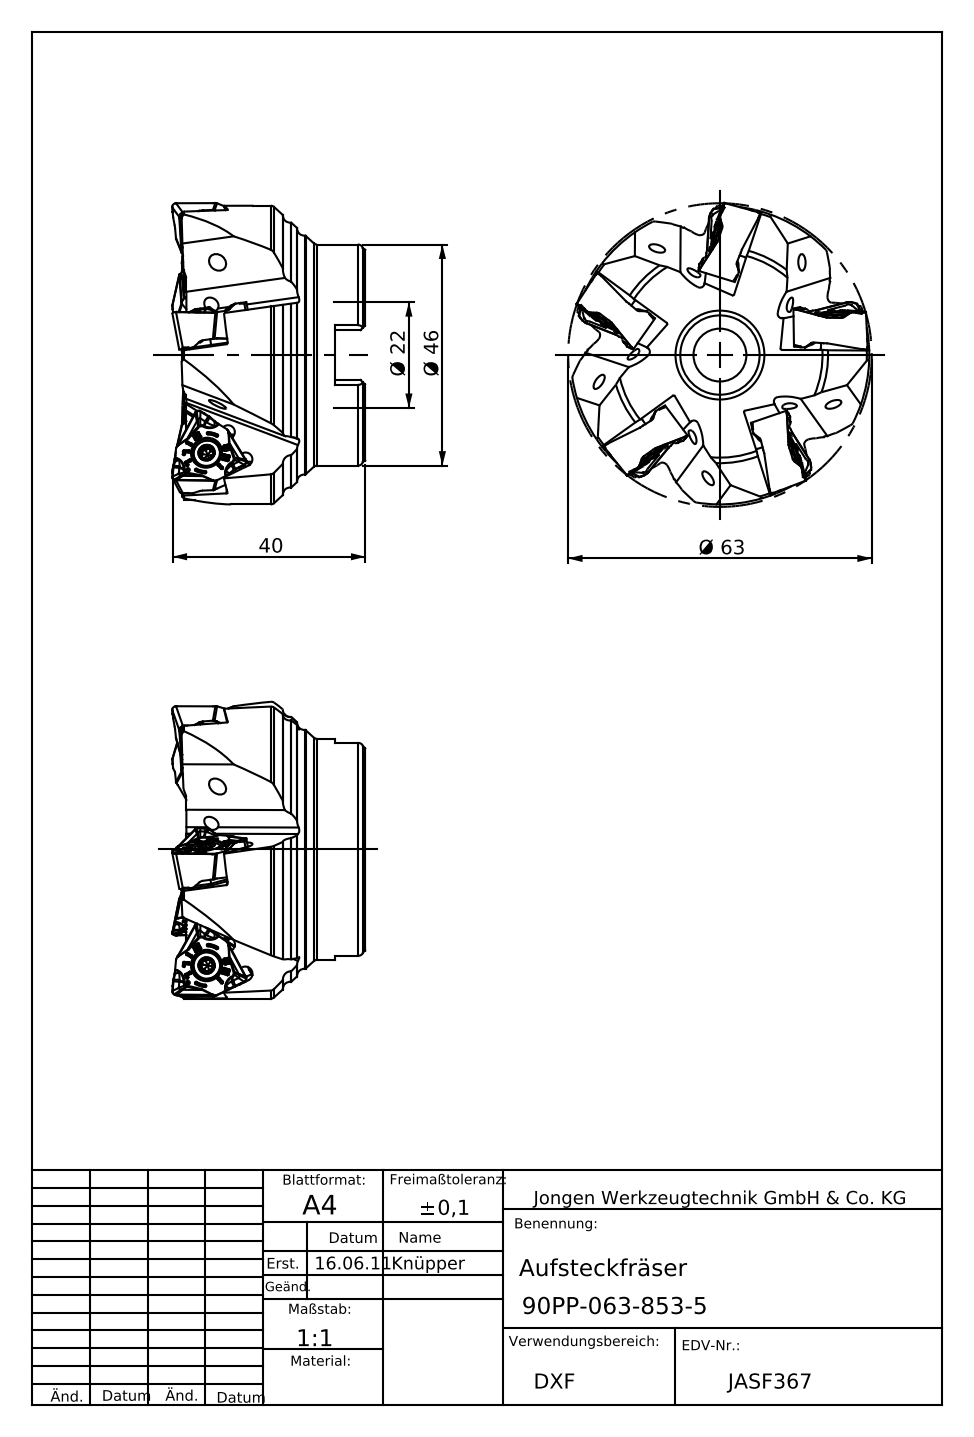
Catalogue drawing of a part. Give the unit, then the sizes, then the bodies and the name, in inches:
Units: inches
Overall size (bounding box): 2.48 × 2.48 × 1.575
Round holes (diameter × count): ⌀0.118 ×5, ⌀0.433 ×1, ⌀0.65 ×1, ⌀0.866 ×1, ⌀0.872 ×1, ⌀0.878 ×1
Round bosses / shafts (diameter × count): ⌀2.48 ×1, ⌀2.447 ×1, ⌀1.811 ×1
Partial cylindrical surfaces — rounded edges, fillets, slot ends (radius × count): R0.012 ×35, R0.059 ×10
Main face-to-face distances: 1.504, 1.467, 0.037, 0.25, 1.217, 1.254, 0.907, 0.657, 0.559, 0.596
Volume: 4.735 in³ · Surface area: 28.77 in²
Bodies: 1 solid, 304 faces (89 planar, 91 cylindrical, 124 other)
Part name (STEP PRODUCT): 90PP-063-853-5
STEP written by: SolidWorks 2011 (AUTOMOTIVE_DESIGN)
